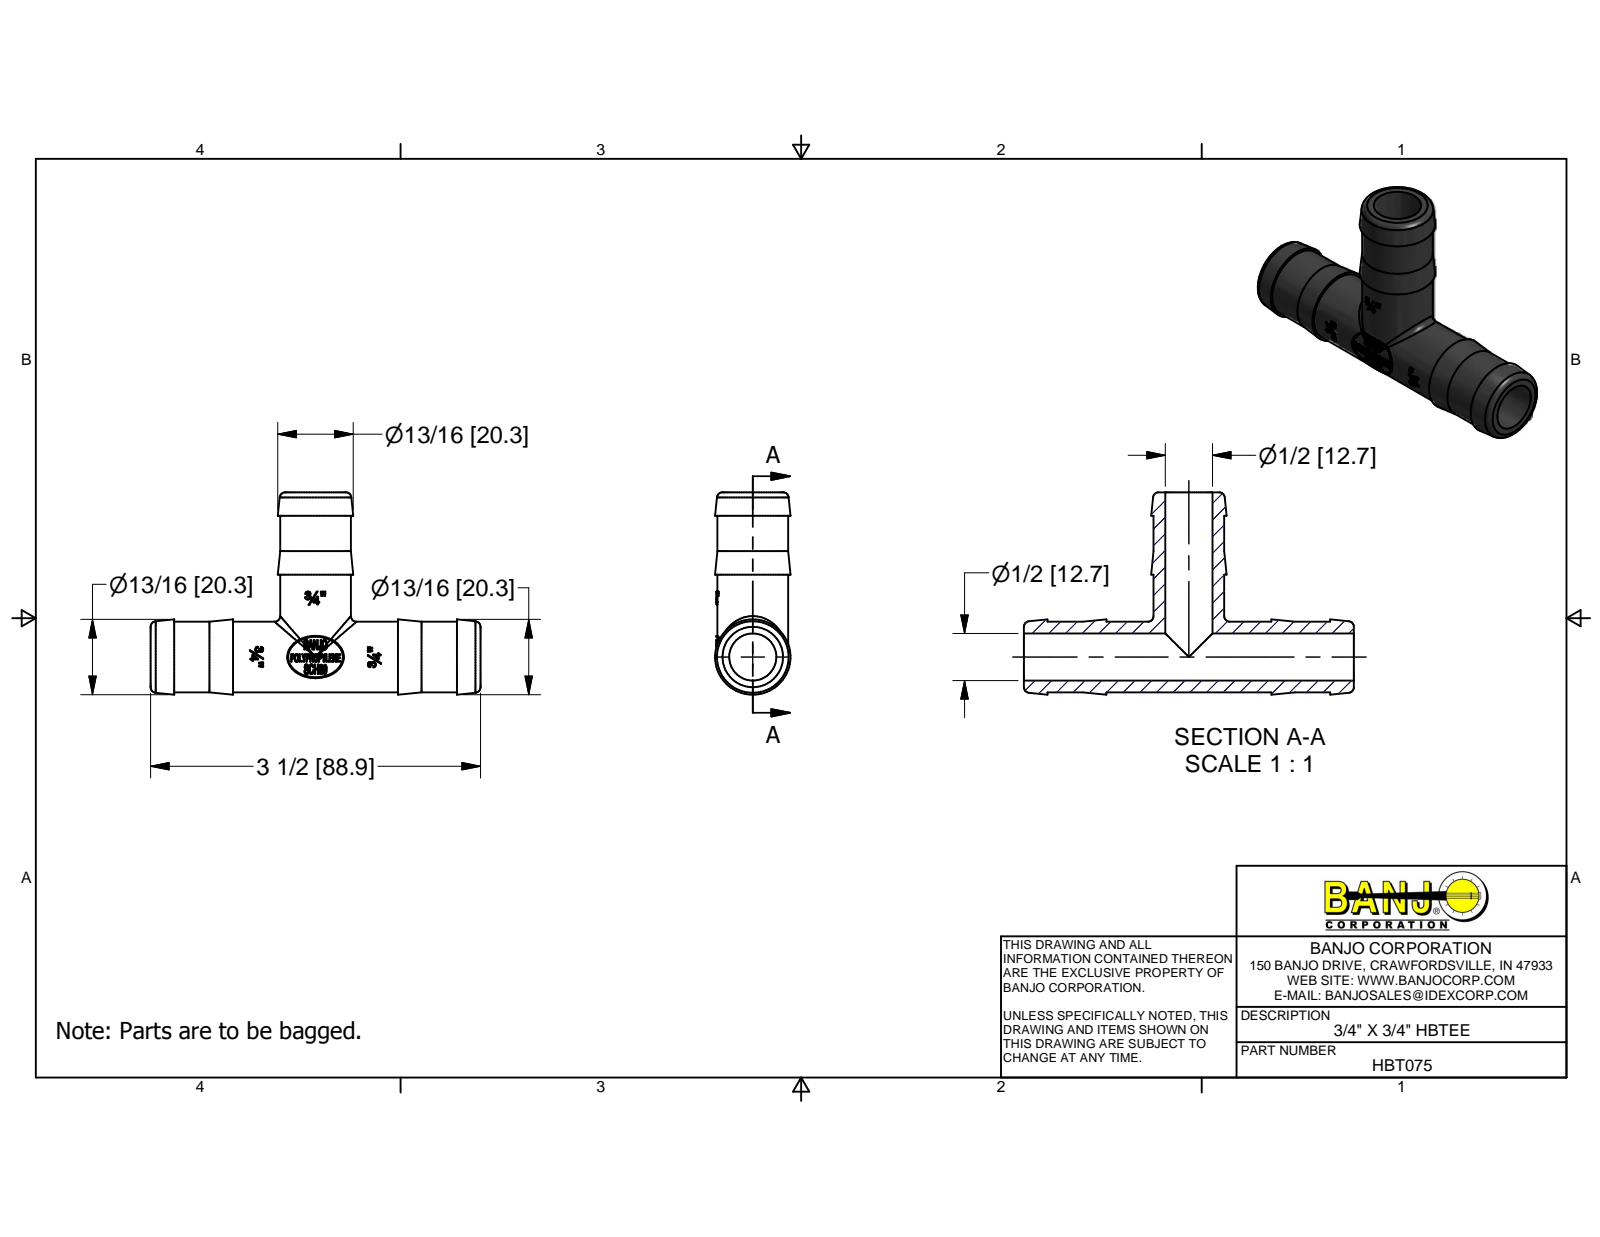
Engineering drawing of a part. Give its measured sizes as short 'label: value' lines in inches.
name: HBT075
written by: Autodesk Inventor 2014 (AUTOMOTIVE_DESIGN)
unit: in
bodies: 1 solid, 542 faces (260 planar, 70 cylindrical, 212 other)
size: 3.5 × 2.15 × 0.8
volume: 1.232 in³; area: 20.22 in²
holes: 2× ⌀0.5
bosses: 2× ⌀0.75
rounds: 2× R0.385
face distances: 0.625, 0.875, 0.25, 3.5, 2.625, 3.25, 2.375, 3, 1.75, 0.071
